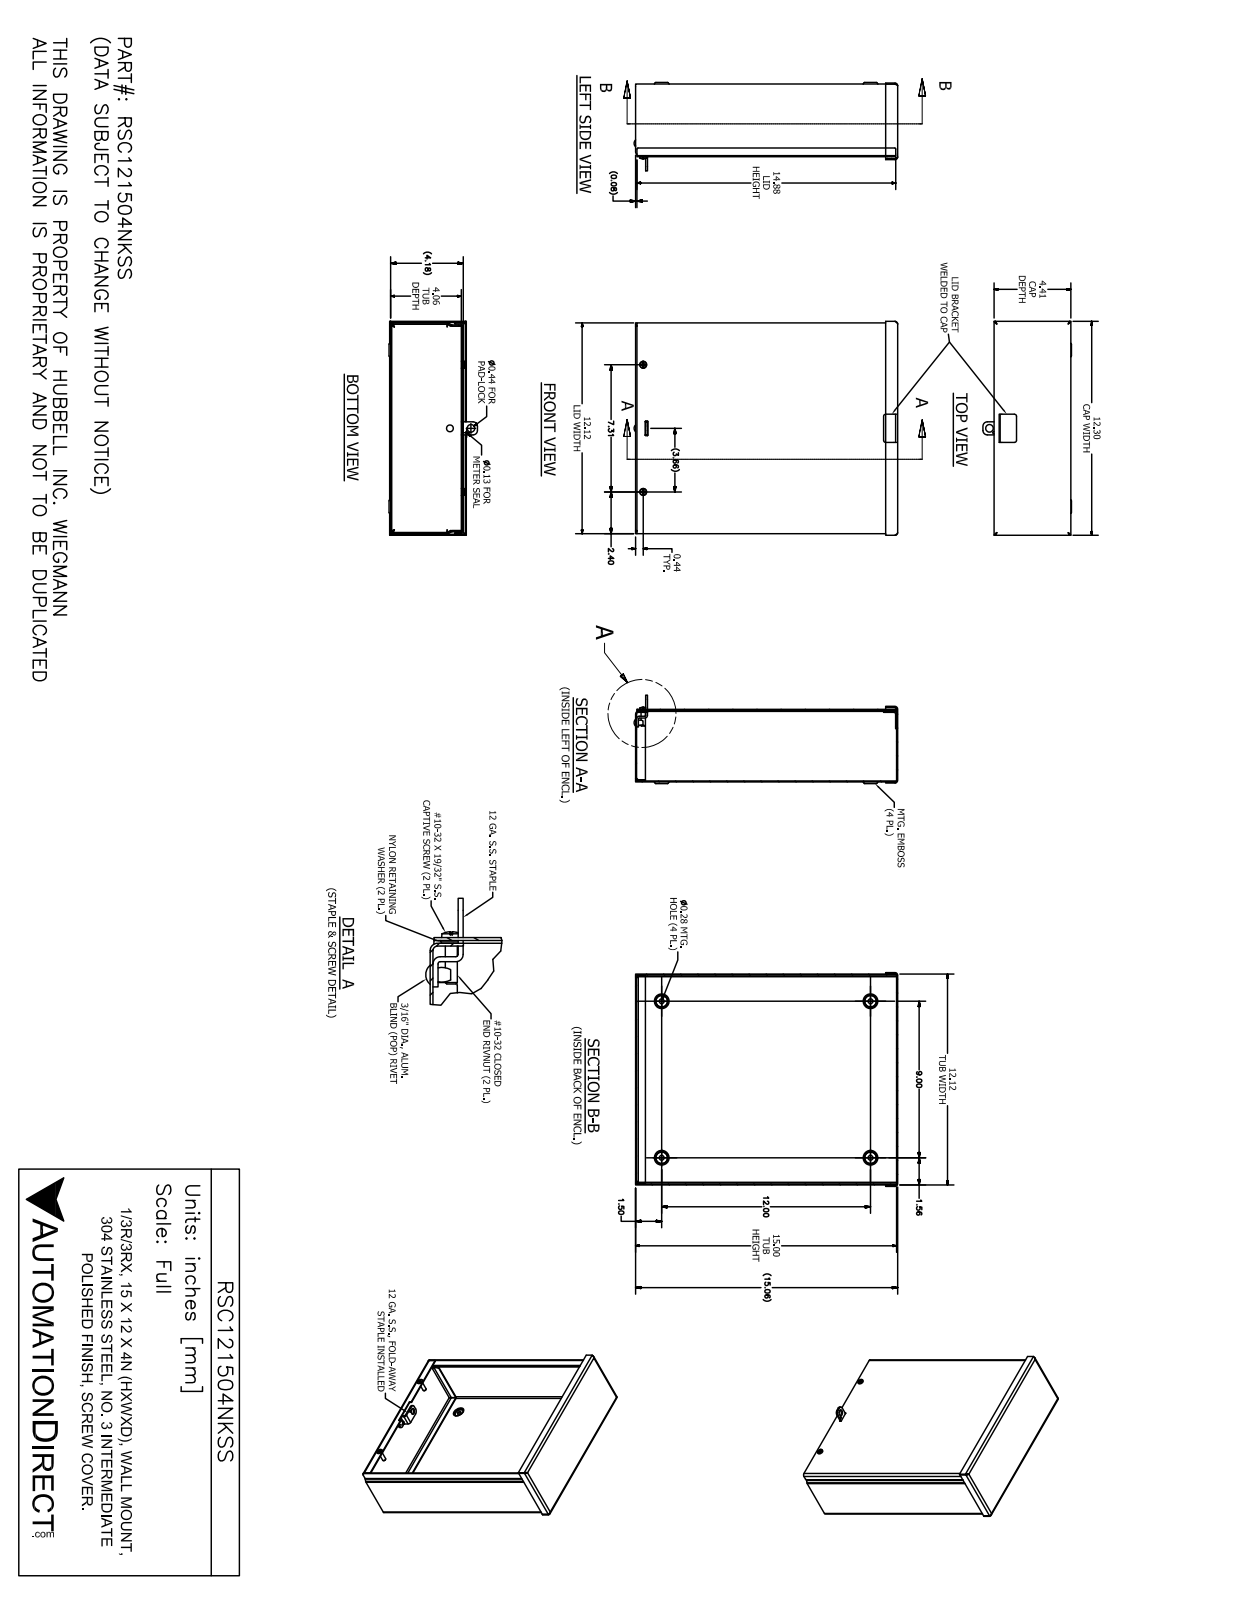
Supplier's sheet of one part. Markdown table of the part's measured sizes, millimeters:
| quantity | value |
| --- | --- |
| part name | RSC121504NKSS |
| STEP written by | SolidWorks 2017 (AUTOMOTIVE_DESIGN) |
| units | millimeters |
| bodies | 13 solids, 383 faces (199 planar, 99 cylindrical, 85 other) |
| overall size | 384.8 × 312.4 × 129.1 |
| volume | 614 700 mm³ |
| surface area | 827 700 mm² |
| round holes (diameter × count) | 6.4 × 4, 7.1 × 4, 4 × 2, 5 × 2, 6.5 × 2, 7.1 × 2, 3.2 × 1, 5 × 1, 5.1 × 1, 11.1 × 1 |
| round bosses / shafts (diameter × count) | 11.5 × 2, 10.3 × 2, 6.3 × 2, 4.2 × 2, 4.7 × 1 |
| partial cylindrical surfaces (radius × count) | 2.4 × 17, 3.9 × 17, 0.8 × 6, 3.2 × 4, 6.4 × 4, 1.2 × 2, 1.3 × 2, 1.6 × 2 |
| main face-to-face distances | 1.5, 104.6, 106.1, 103.1, 306.3, 381, 307.8, 304.8, 379.5, 382.5 |
| hole center spacings | 34.5, 35.1, 185.8, 208.9, 209, 228.6, 304.8, 332.5 |
